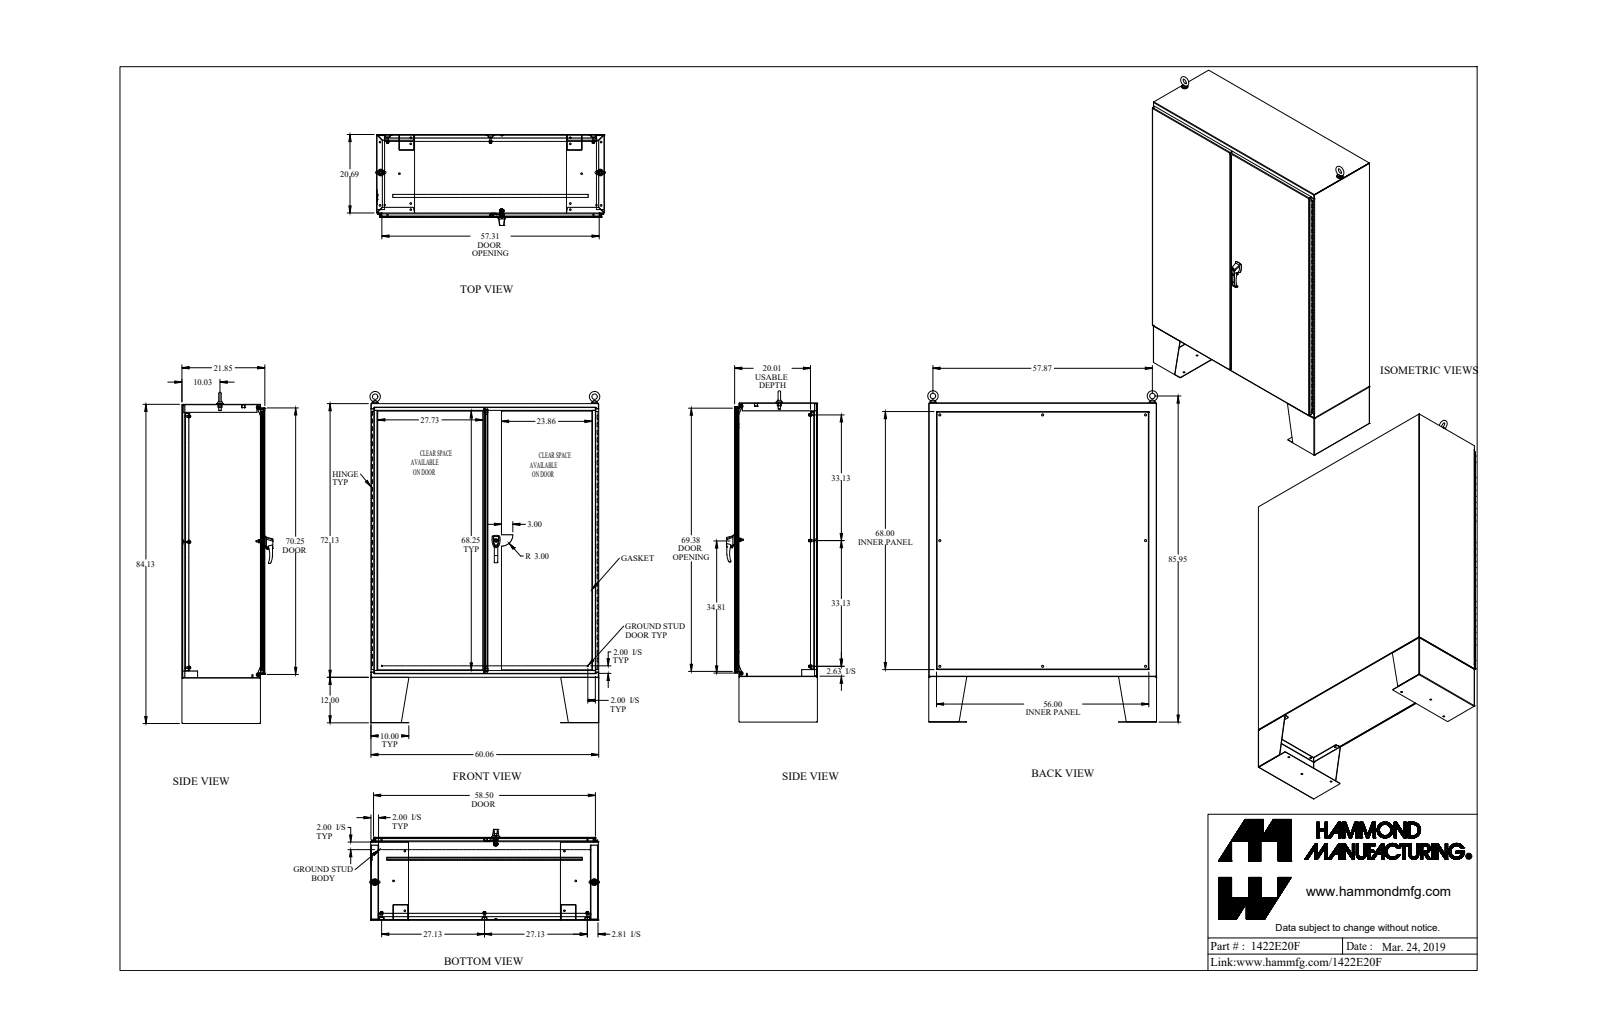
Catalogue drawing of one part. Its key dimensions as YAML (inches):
part_name: "1422E20F_Default"
step_written_by: "SolidWorks 2019 (CONFIG_CONTROL_DESIGN)"
units: inches
bodies: {solids: 92, faces: 2997, planar: 1372, cylindrical: 1378, other: 247}
overall_size: [87.778, 61.121, 23.963]
volume: 2356
surface_area: 44436
round_holes:
  - {diameter: 0.304, count: 24}
  - {diameter: 0.437, count: 14}
  - {diameter: 0.307, count: 9}
  - {diameter: 0.563, count: 8}
  - {diameter: 0.445, count: 6}
  - {diameter: 0.11, count: 2}
  - {diameter: 0.25, count: 2}
  - {diameter: 0.257, count: 2}
  - {diameter: 0.28, count: 2}
  - {diameter: 0.281, count: 2}
  - {diameter: 0.313, count: 2}
  - {diameter: 0.39, count: 2}
round_bosses_or_shafts:
  - {diameter: 1, count: 10}
  - {diameter: 0.65, count: 8}
  - {diameter: 0.375, count: 8}
  - {diameter: 0.33, count: 8}
  - {diameter: 0.281, count: 6}
  - {diameter: 0.25, count: 4}
  - {diameter: 1.75, count: 2}
  - {diameter: 1.5, count: 2}
partial_cylinders:
  - {radius: 0.048, count: 32}
  - {radius: 0.143, count: 32}
  - {radius: 0.125, count: 22}
  - {radius: 0.018, count: 16}
  - {radius: 0.06, count: 14}
  - {radius: 0.116, count: 12}
  - {radius: 0.187, count: 9}
  - {radius: 0.05, count: 8}
face_to_face_distances: [0.095, 0.125, 21.753, 21.628, 21.723, 21.848, 0.125, 1.687, 20.036, 19.941]
hole_center_spacings: [6, 12, 58.7, 59.613, 18, 61.104, 24, 63.132]
